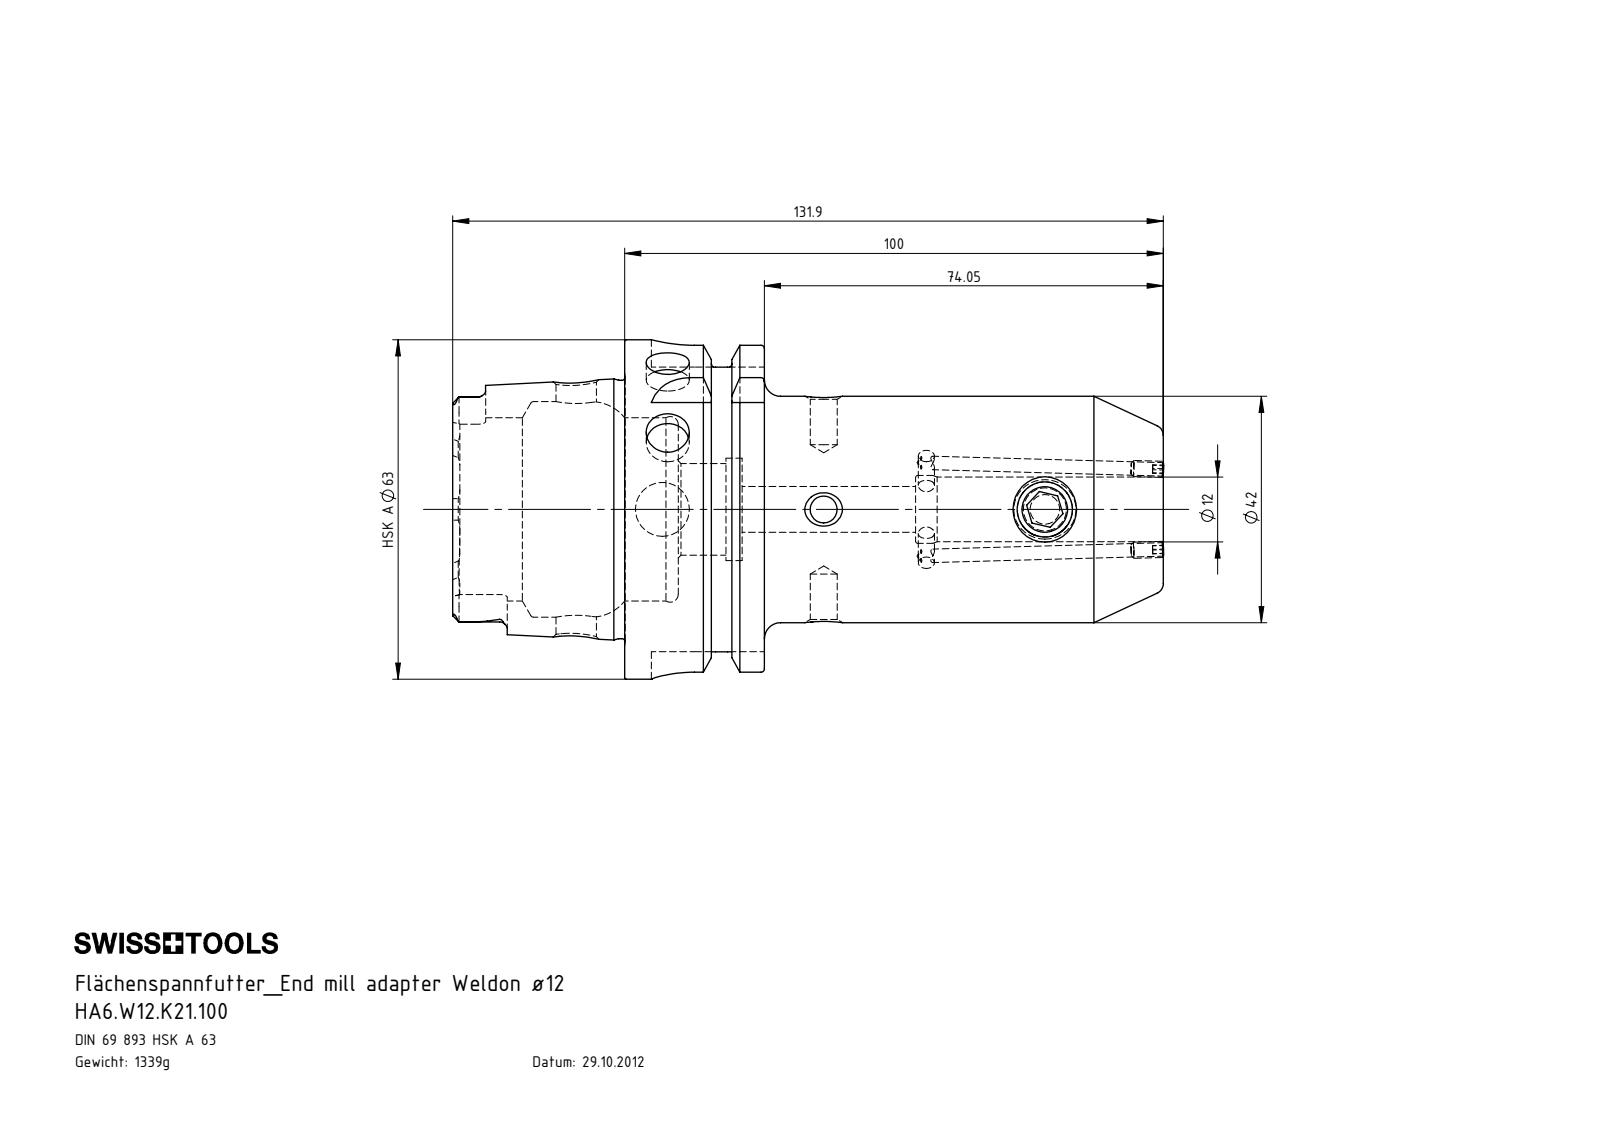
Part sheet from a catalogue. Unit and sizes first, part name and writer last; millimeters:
Units: millimetres
Overall size (bounding box): 131.95 × 63 × 63
Round holes (diameter × count): ⌀2.5 ×2, ⌀5 ×2, ⌀8 ×2, ⌀3 ×1, ⌀7.5 ×1, ⌀8.5 ×1, ⌀10 ×1, ⌀10.25 ×1, ⌀12 ×1, ⌀12.6 ×1, ⌀17 ×1, ⌀19 ×1
Round bosses / shafts (diameter × count): ⌀3 ×2, ⌀63 ×1, ⌀54.95 ×1, ⌀47.94 ×1, ⌀42 ×1
Partial cylindrical surfaces — rounded edges, fillets, slot ends (radius × count): R1.4 ×6, R2.88 ×4, R8 ×4
Main face-to-face distances: 25.95, 16, 9.95, 100, 90.05, 74.05, 31.9, 41.85, 57.85, 131.9
Hole centre spacings: 29.95, 41.05, 45.95, 71
Volume: 170 530 mm³ · Surface area: 36 410 mm²
Bodies: 4 solids, 286 faces (77 planar, 81 cylindrical, 128 other)
Part name (STEP PRODUCT): HA6-W12.K21.100; ERU-CJ2.001.006; W12-ER1.001.016_zum Wuchten; HA6-W12.K21.100_A_Fertigbearbeitung
STEP written by: SolidWorks 2012 (CONFIG_CONTROL_DESIGN)
